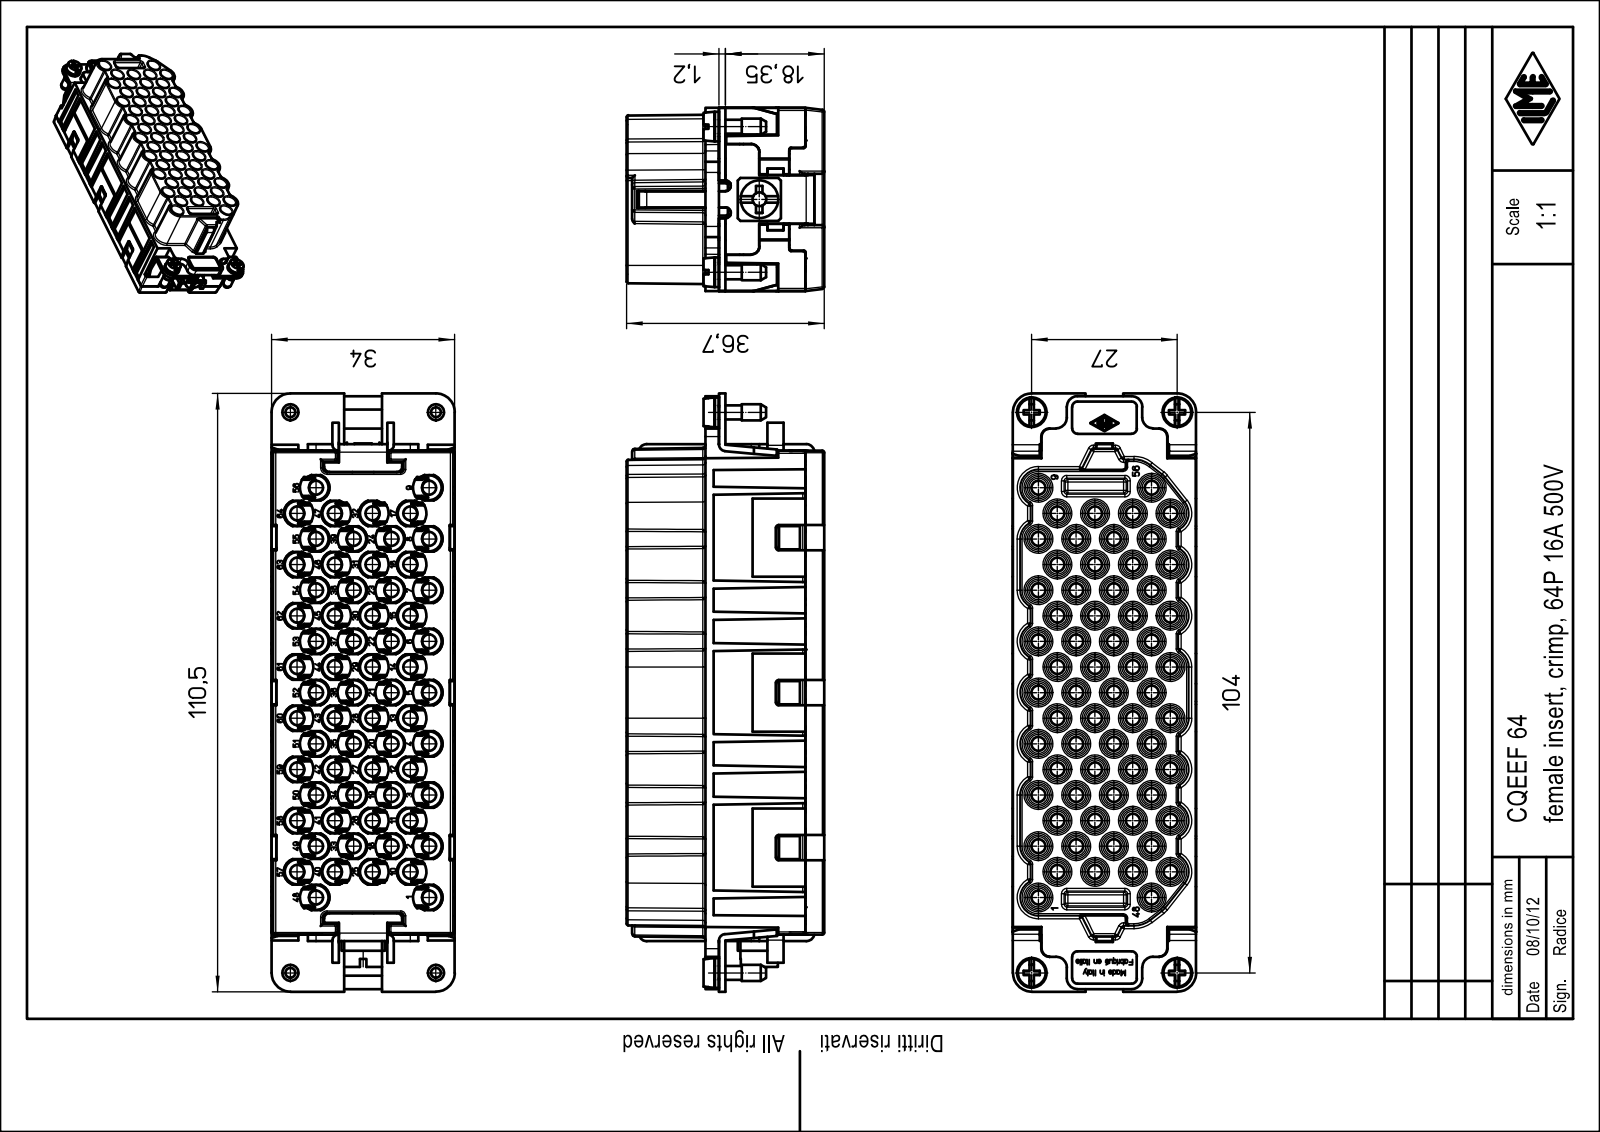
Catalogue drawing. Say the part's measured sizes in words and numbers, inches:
The part is named "CQEEF_64". Its 3-D file was written by "Creo Elements/Direct Modeling 18.0B 02-Dec-2011 (C) Parametric Technology GmbH (AUTOMOTIVE_DESIGN)". It is 1 solid with 7689 faces: 7083 planar, 460 cylindrical and 146 other. Overall it measures 4.37 by 1.445 by 1.339 inches. Its volume is 3.508 cubic inches and its surface area 89.2 square inches. Round holes: 64 of diameter 0.102, 64 of diameter 0.197, 4 of diameter 0.11, 1 of diameter 0.102, 1 of diameter 0.118. Round bosses or shafts: 4 of diameter 0.217, 4 of diameter 0.118, 4 of diameter 0.102, 1 of diameter 0.276, 1 of diameter 0.236. Partial cylindrical surfaces (rounded edges, fillets, slot ends): 64 of radius 0.118, 18 of radius 0.039, 17 of radius 0.136, 15 of radius 0.004, 10 of radius 0.059, 8 of radius 0.079, 4 of radius 0.047, 4 of radius 0.138. The main face-to-face distances are 1.303, 0.035, 1.445, 0.047, 1.339, 0.244, 0.722, 1.201, 1.268, 0.333. The hole center spacings are 0.232, 0.465, 0.578, 0.454, 0.374, 0.276, 0.714, 0.797.
